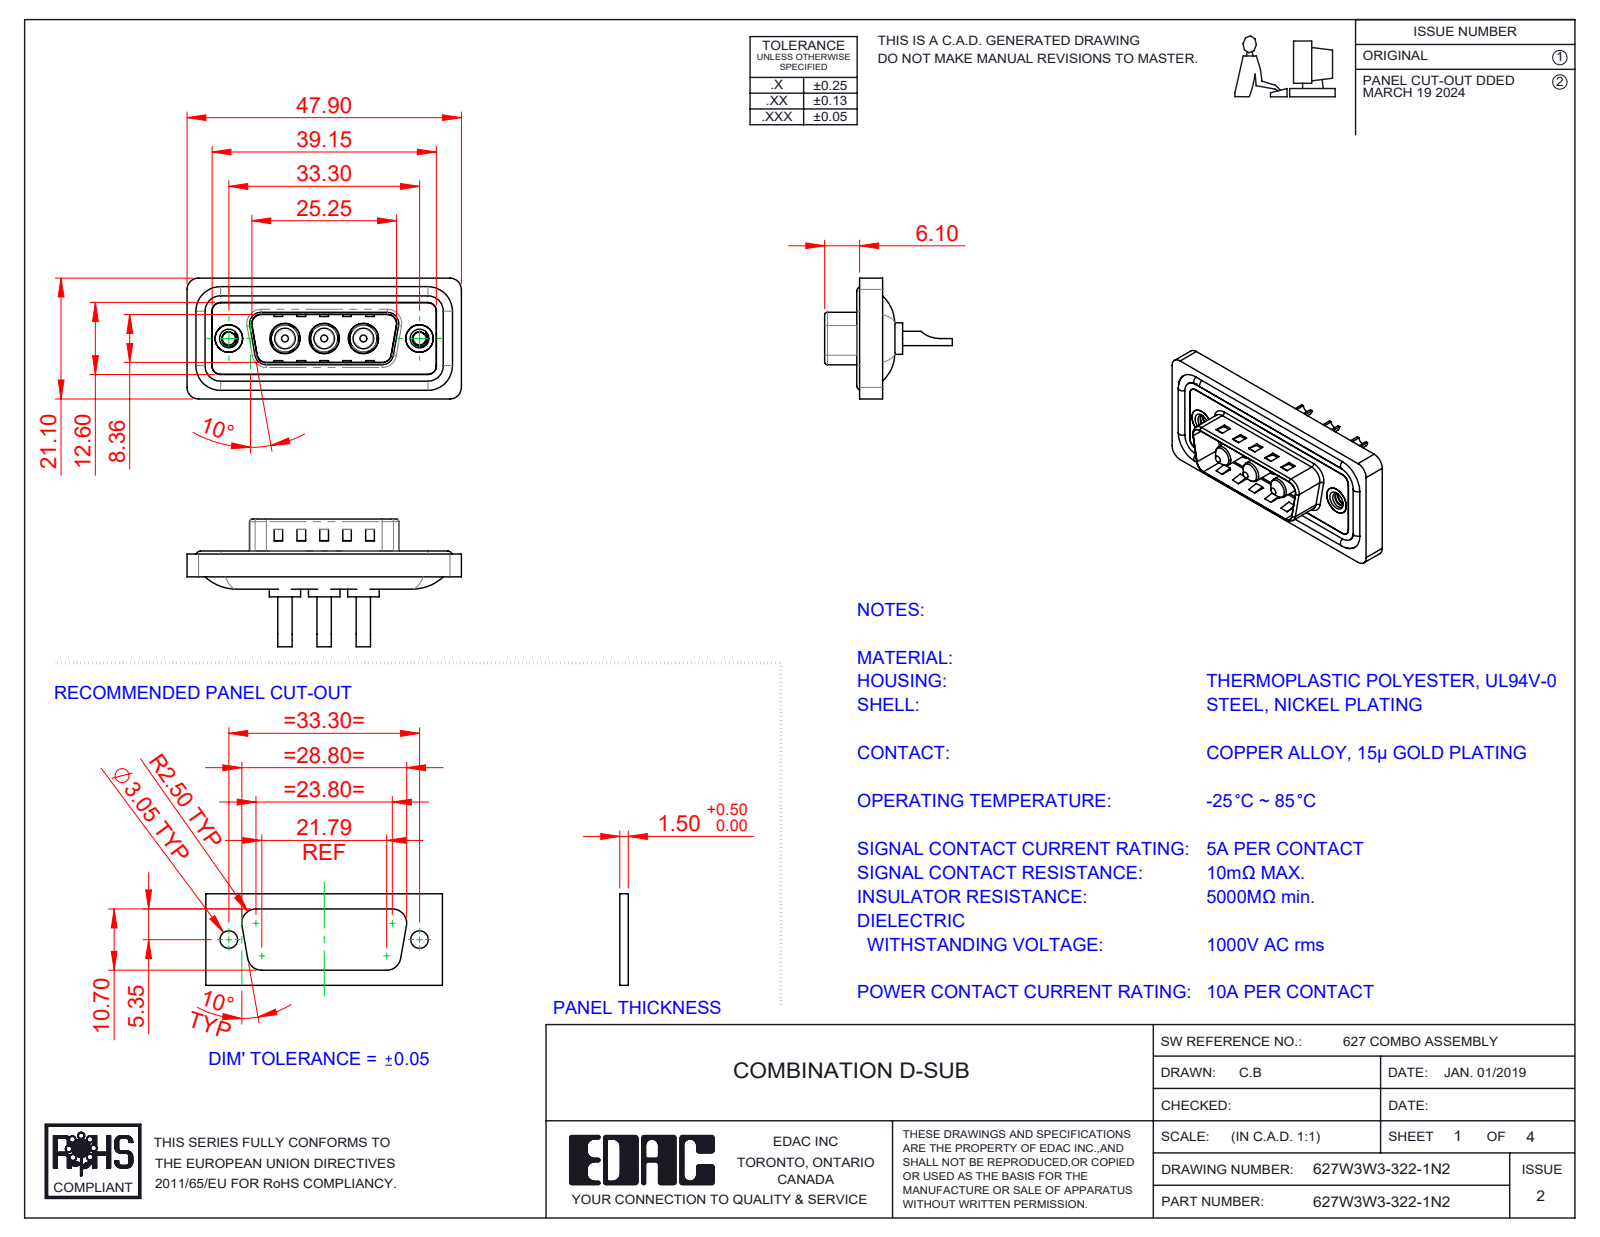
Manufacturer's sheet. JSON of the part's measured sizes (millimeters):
{"part_name": "627Combo Threaded Rivet_2; Power Pin_10A SC; 627Combo Housing_3W3; 627Combo Waterproof Housing_15 Contacts (+3 more)", "step_written_by": "SolidWorks 2023 (CONFIG_CONTROL_DESIGN)", "units": "millimeters", "bodies": {"solids": 13, "faces": 582, "planar": 213, "cylindrical": 250, "other": 119}, "overall_size": [47.9, 22.3, 21.1], "volume_mm3": 5577, "surface_area_mm2": 8897, "round_holes": [[1.7, 3], [4.85, 3], [5.3, 3], [2.26, 2], [4, 2], [4.8, 2], [5, 2]], "round_bosses_or_shafts": [[1.6, 4], [5.5, 3], [5.2, 3], [4.75, 3], [3.75, 3], [3.6, 3], [2.5, 3], [4.9, 2]], "partial_cylinders_radius": [[1.5, 26], [2, 20], [0.5, 8], [1.6, 8], [0.25, 4], [0.6, 4], [0.65, 4], [0.9, 4]], "face_to_face_distances": [0.4, 1.1, 1.5, 0.5, 1.6, 3.1, 2.9, 4, 0.82, 9.58], "hole_center_spacings": [6.85, 9.8, 16.65, 23.5, 13.7, 33.3]}
